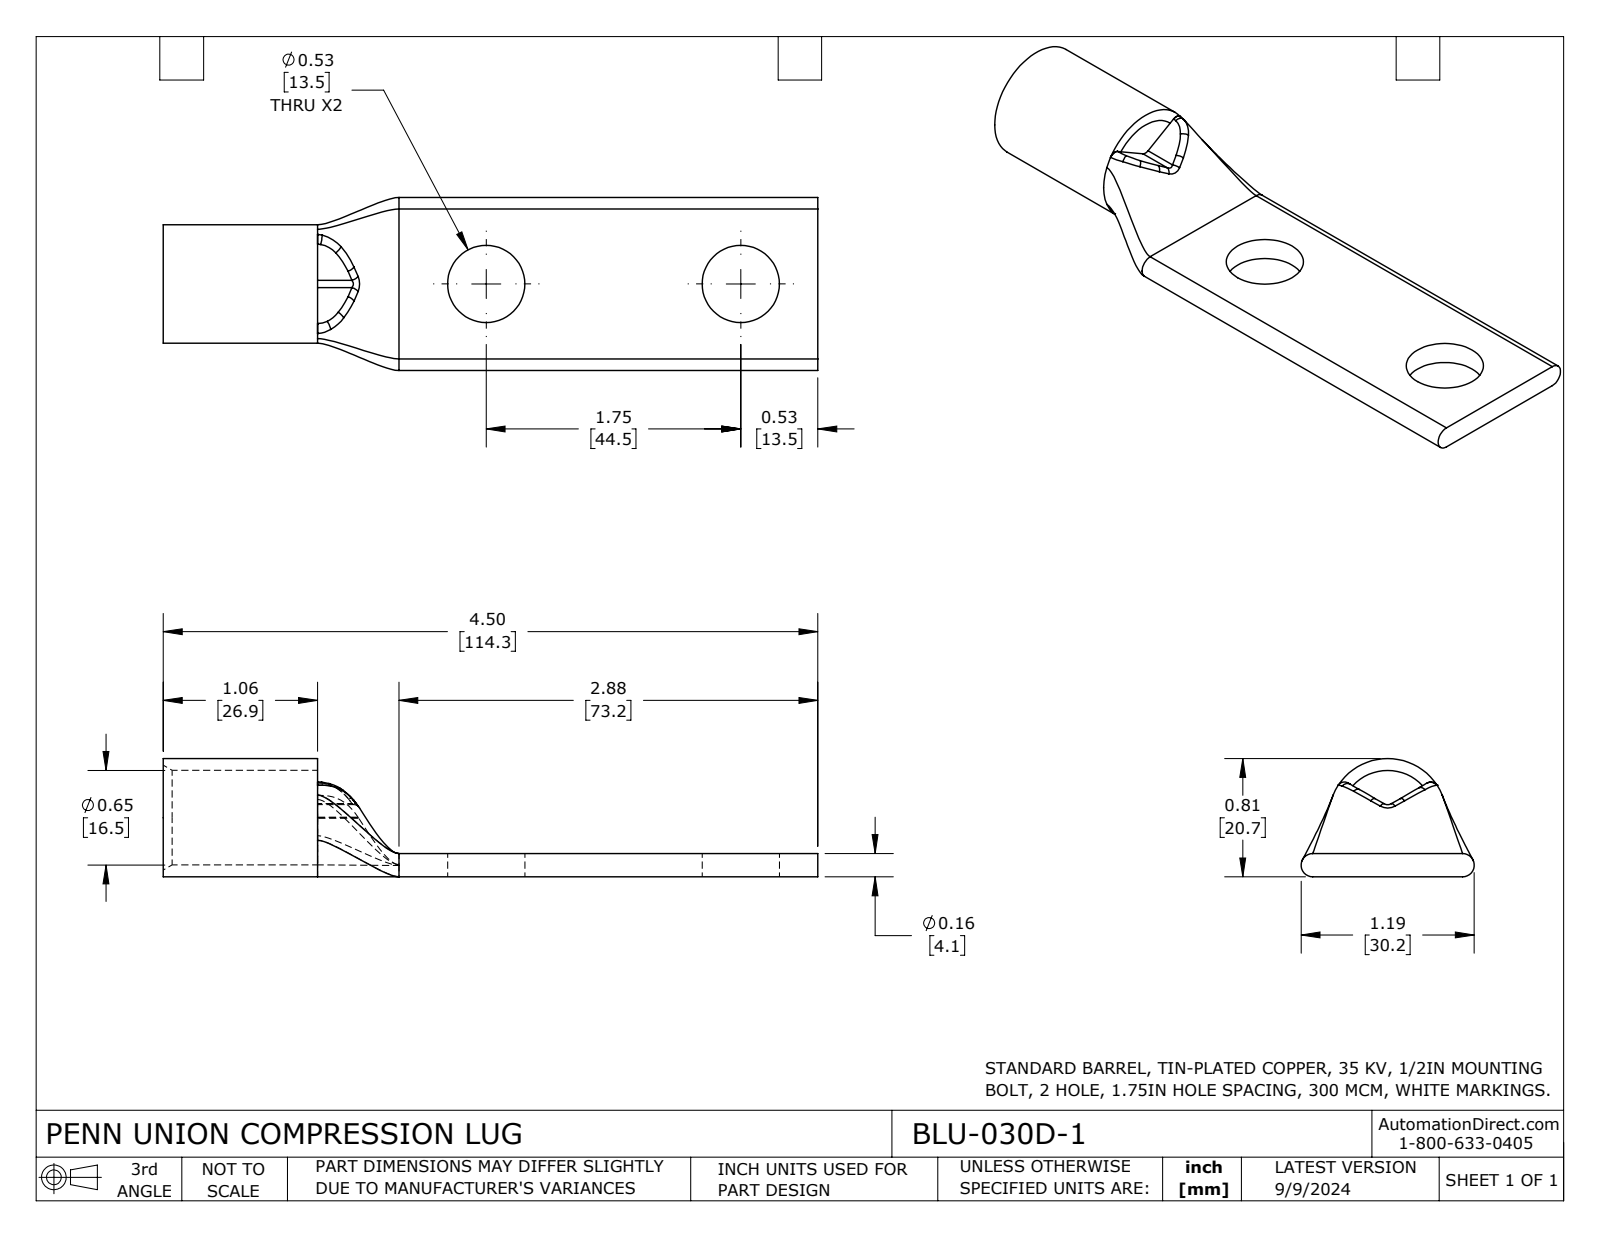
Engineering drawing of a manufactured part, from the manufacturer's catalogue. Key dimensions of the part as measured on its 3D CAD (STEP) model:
Part name (STEP PRODUCT): BLU-030D-1
STEP written by: SolidWorks 2023 (CONFIG_CONTROL_DESIGN)
Units: inches
Bodies: 1 solid, 45 faces (11 planar, 13 cylindrical, 21 other)
Overall size (bounding box): 4.5 × 1.19 × 0.813
Volume: 0.756 in³ · Surface area: 15.21 in²
Round holes (diameter × count): ⌀0.531 ×2, ⌀0.65 ×1
Round bosses / shafts (diameter × count): ⌀0.813 ×1
Partial cylindrical surfaces — rounded edges, fillets, slot ends (radius × count): R0.05 ×2, R0.08 ×2
Main face-to-face distances: 0.16, 4.5, 1.06, 3.44, 0.081, 1.62, 0.56, 2.88
Hole centre spacings: 1.75
